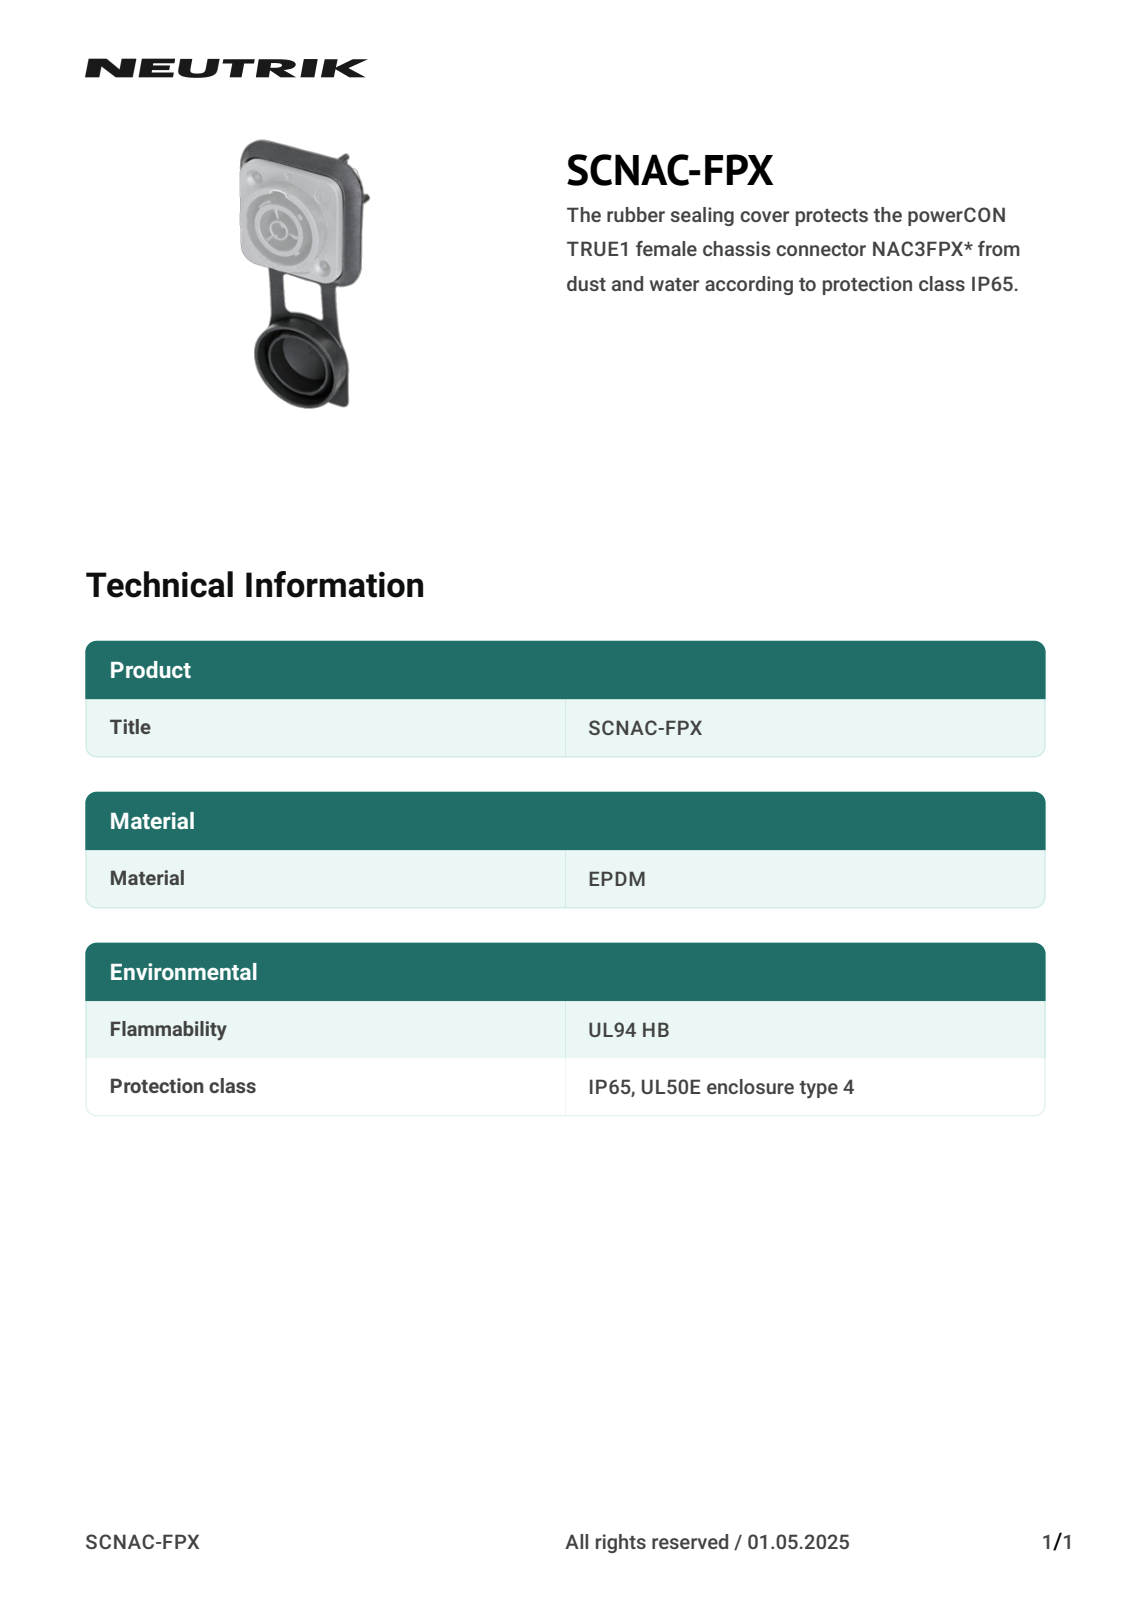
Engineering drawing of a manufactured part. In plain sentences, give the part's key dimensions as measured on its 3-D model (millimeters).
The part is named "SCNAC-FPX". Its 3-D file was written by "CREO PARAMETRIC BY PTC INC, 2019080 (CONFIG_CONTROL_DESIGN)". It is 1 solid with 776 faces: 463 planar, 69 cylindrical and 244 other. Overall it measures 90.5 by 43.6 by 12.2 millimeters. Its volume is 8 095 cubic millimeters and its surface area 6 877 square millimeters. Round holes: 2 of diameter 3.1, 2 of diameter 3.5, 1 of diameter 28. Round bosses or shafts: 1 of diameter 30.8. Partial cylindrical surfaces (rounded edges, fillets, slot ends): 8 of radius 0.5, 7 of radius 1, 7 of radius 2, 4 of radius 0.2, 4 of radius 0.3, 4 of radius 0.74, 4 of radius 5.6, 4 of radius 6.2. The main face-to-face distances are 3.15, 1, 2.15, 0.8, 3.95, 1.8, 2, 5.15, 3, 1.2. The hole center spacings are 17.25, 34.51.
